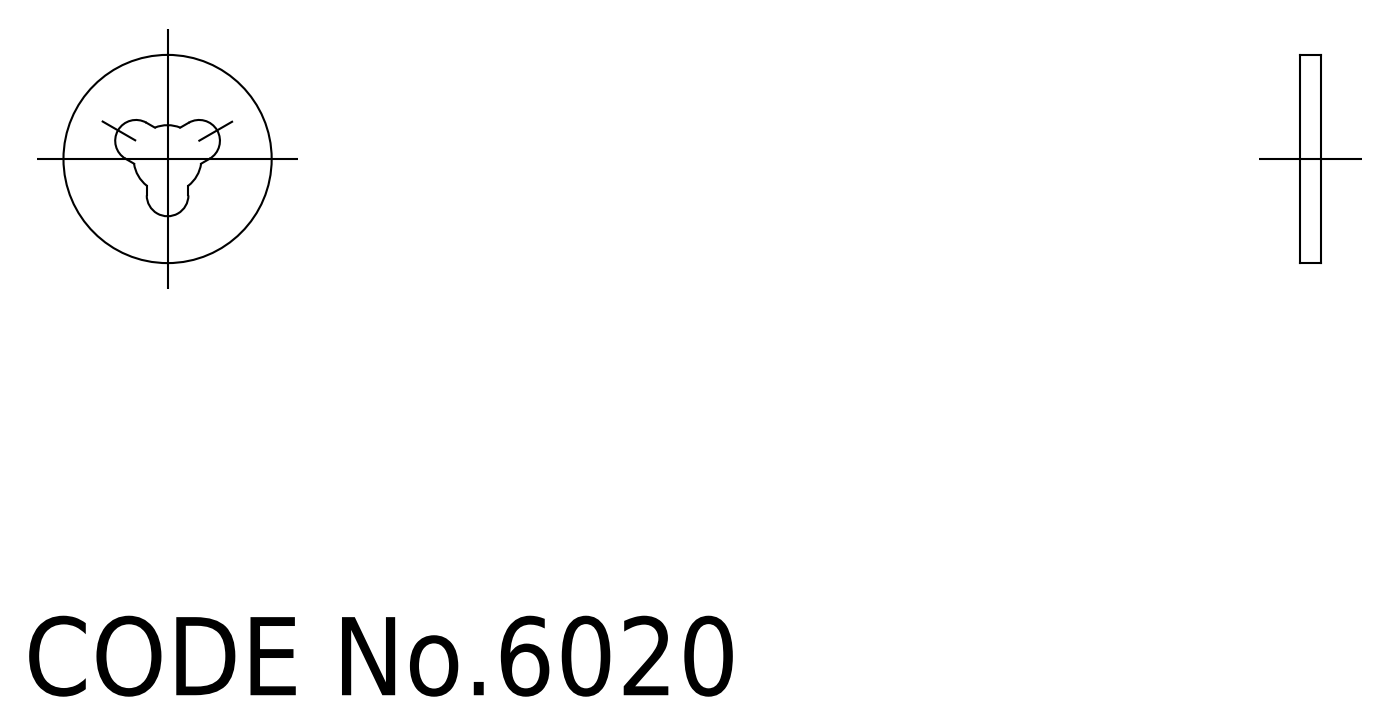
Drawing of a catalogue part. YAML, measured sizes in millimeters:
part_name: "washer"
step_written_by: "CADfix (AUTOMOTIVE_DESIGN)"
units: millimeters
bodies: {solids: 1, faces: 16, planar: 0, cylindrical: 0, other: 16}
overall_size: [8, 8, 0.8]
volume: 33
surface_area: 112
